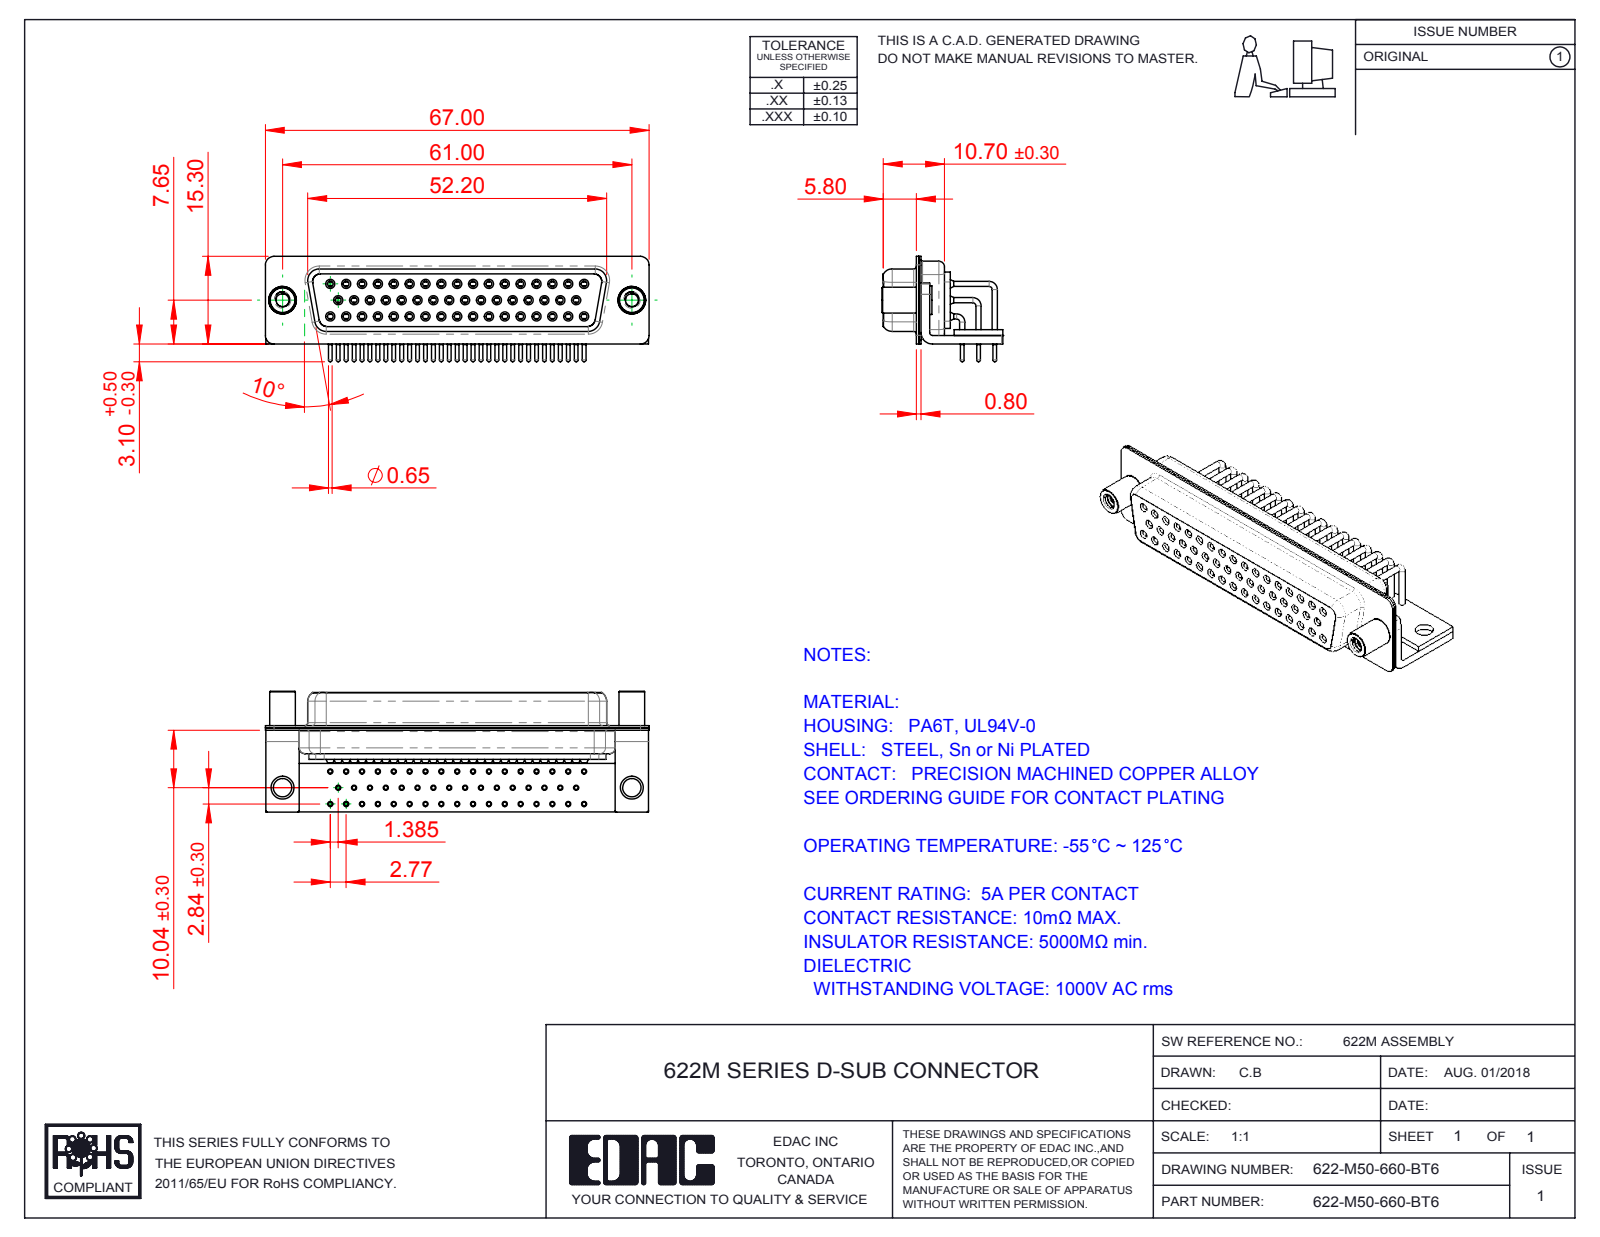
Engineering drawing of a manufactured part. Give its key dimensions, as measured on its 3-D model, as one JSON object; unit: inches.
{"part_name": "622M Shell Rear_50 Contacts; 622M Shell Front_50 Contacts; 622M Housing_50 Contacts; 622-M50-660-BT6 (+6 more)", "step_written_by": "SolidWorks 2016 (CONFIG_CONTROL_DESIGN)", "units": "inches", "bodies": {"solids": 58, "faces": 3129, "planar": 845, "cylindrical": 1451, "other": 833}, "overall_size": [2.638, 0.831, 0.724], "volume_in3": 0.48, "surface_area_in2": 28.57, "round_holes": [[0.035, 50], [0.039, 50], [0.043, 50], [0.067, 50], [0.071, 50], [0.079, 50], [0.089, 2], [0.126, 2], [0.157, 2], [0.189, 2]], "round_bosses_or_shafts": [[0.035, 59], [0.063, 50], [0.059, 50], [0.026, 50], [0.197, 2], [0.193, 2], [0.177, 2]], "partial_cylinders_radius": [[0.01, 16], [0.059, 16], [0.079, 13], [0.053, 8], [0.063, 8], [0.02, 5], [0.024, 4], [0.026, 4]], "face_to_face_distances": [0.016, 0.039, 0.087, 0.033, 0.053, 0.467, 0.482, 0.228, 0.031, 0.232], "hole_center_spacings": [0.109, 0.124, 0.218, 0.327, 0.436, 0.545, 0.654, 0.763]}
